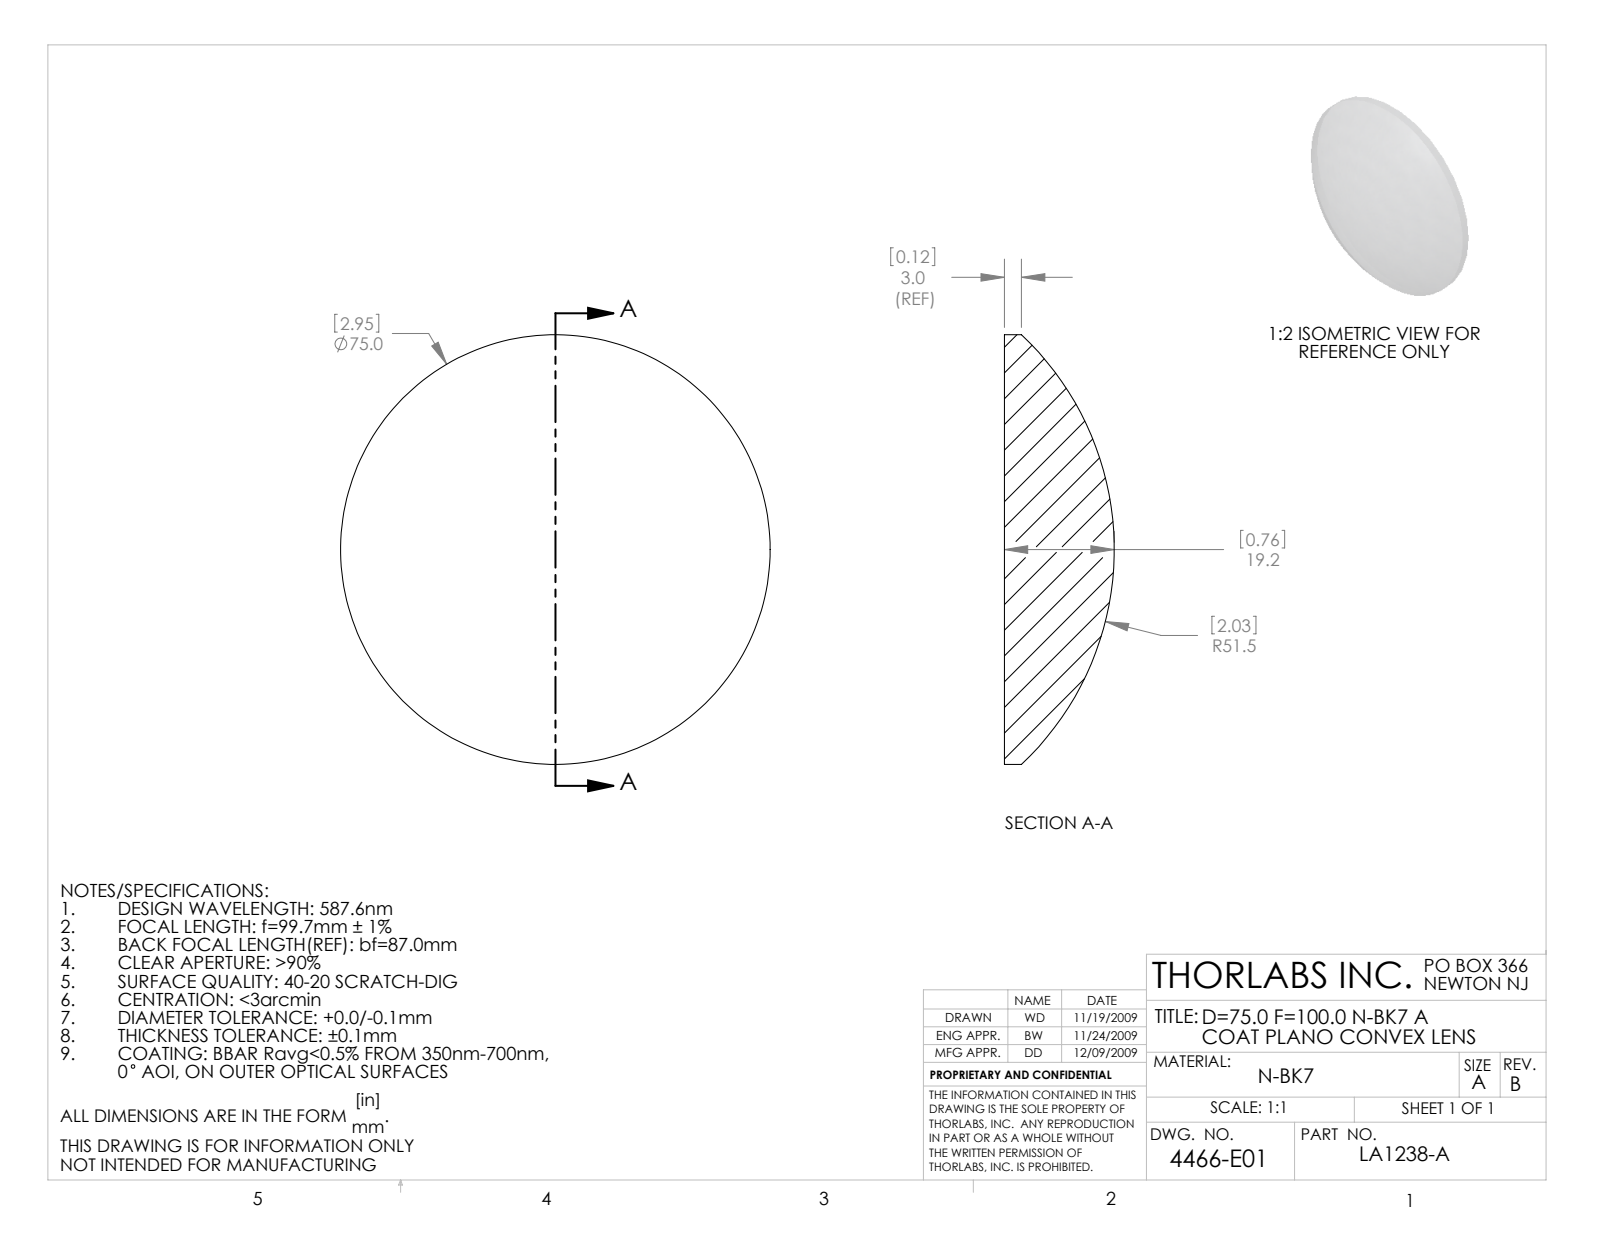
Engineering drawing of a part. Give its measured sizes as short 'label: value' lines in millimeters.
name: 4466-E0W
written by: SolidWorks 2009 (AUTOMOTIVE_DESIGN)
unit: mm
bodies: 1 solid, 5 faces (1 planar, 2 cylindrical, 2 other)
size: 75 × 75 × 19.19
volume: 51 218 mm³; area: 10 365 mm²
bosses: 1× ⌀75
